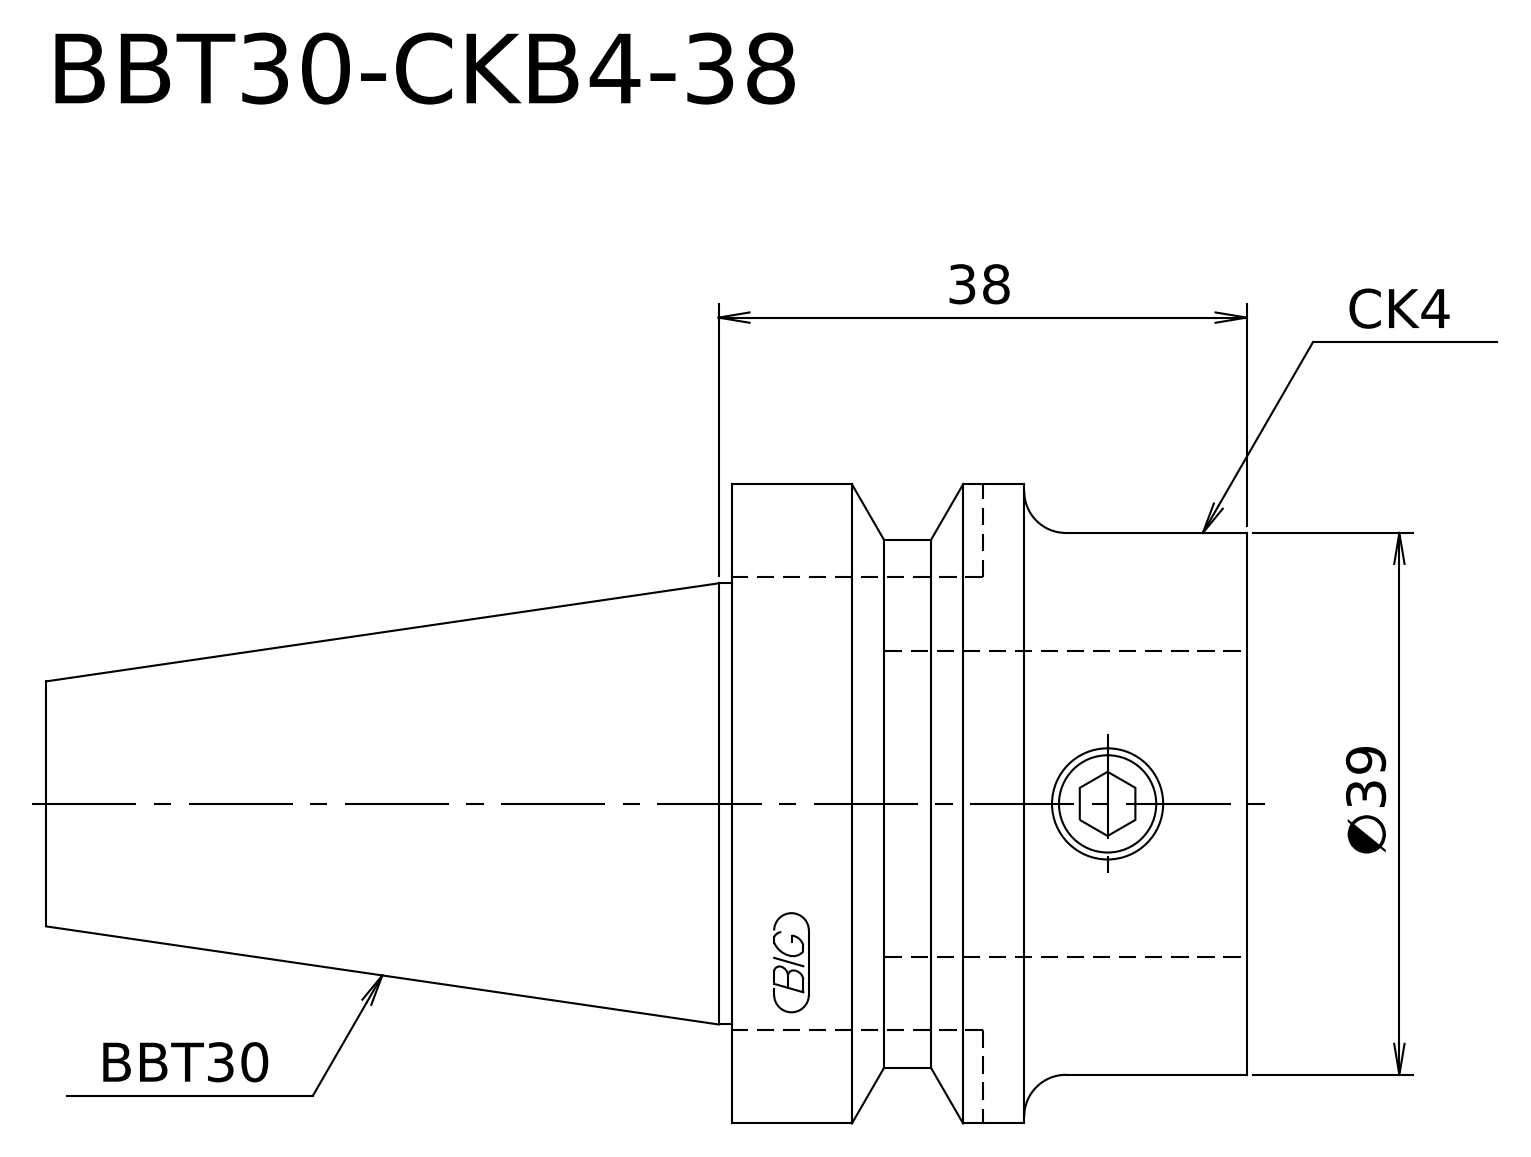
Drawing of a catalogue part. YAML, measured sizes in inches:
step_written_by: "Kubotek KeyCreator V8.5.1 (14335) (CONFIG_CONTROL_DESIGN)"
units: inches
bodies: {solids: 1, faces: 13, planar: 4, cylindrical: 5, other: 4}
overall_size: [3.402, 1.811, 1.811]
volume: 4.643
surface_area: 18.51
round_bosses_or_shafts:
  - {diameter: 1.811, count: 1}
  - {diameter: 1.535, count: 1}
  - {diameter: 1.496, count: 1}
  - {diameter: 1.25, count: 1}
face_to_face_distances: [1.457, 3.402, 1.945, 0.63, 0.827, 2.772]
